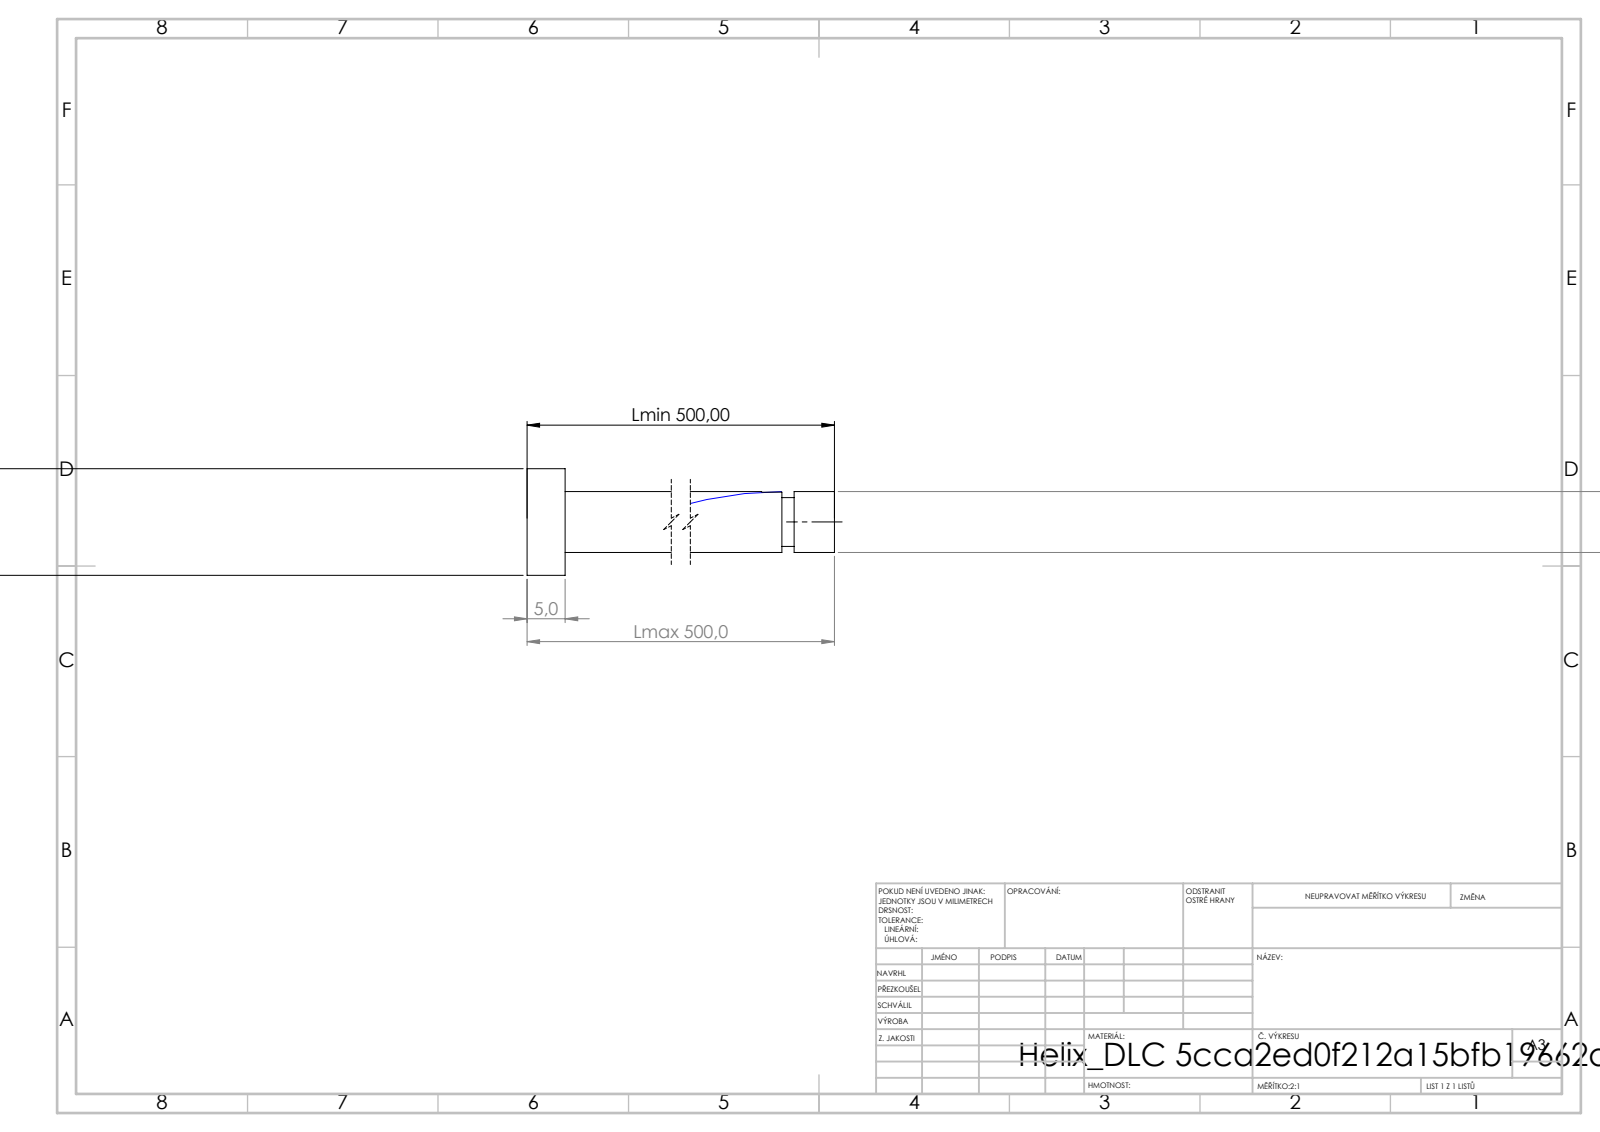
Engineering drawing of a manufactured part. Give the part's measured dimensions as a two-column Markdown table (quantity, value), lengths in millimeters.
| quantity | value |
| --- | --- |
| STEP written by | SolidWorks 2019 (CONFIG_CONTROL_DESIGN) |
| units | millimeters |
| bodies | 1 solid, 16 faces (6 planar, 9 cylindrical, 1 other) |
| overall size | 500 × 14 × 14 |
| volume | 30 966 mm³ |
| surface area | 17 385 mm² |
| round bosses / shafts (diameter × count) | 14 × 1, 8 × 1, 6.4 × 1 |
| main face-to-face distances | 5, 500, 495, 494.7, 489.7, 5.3, 493.1, 488.1, 1.6, 6.9 |
